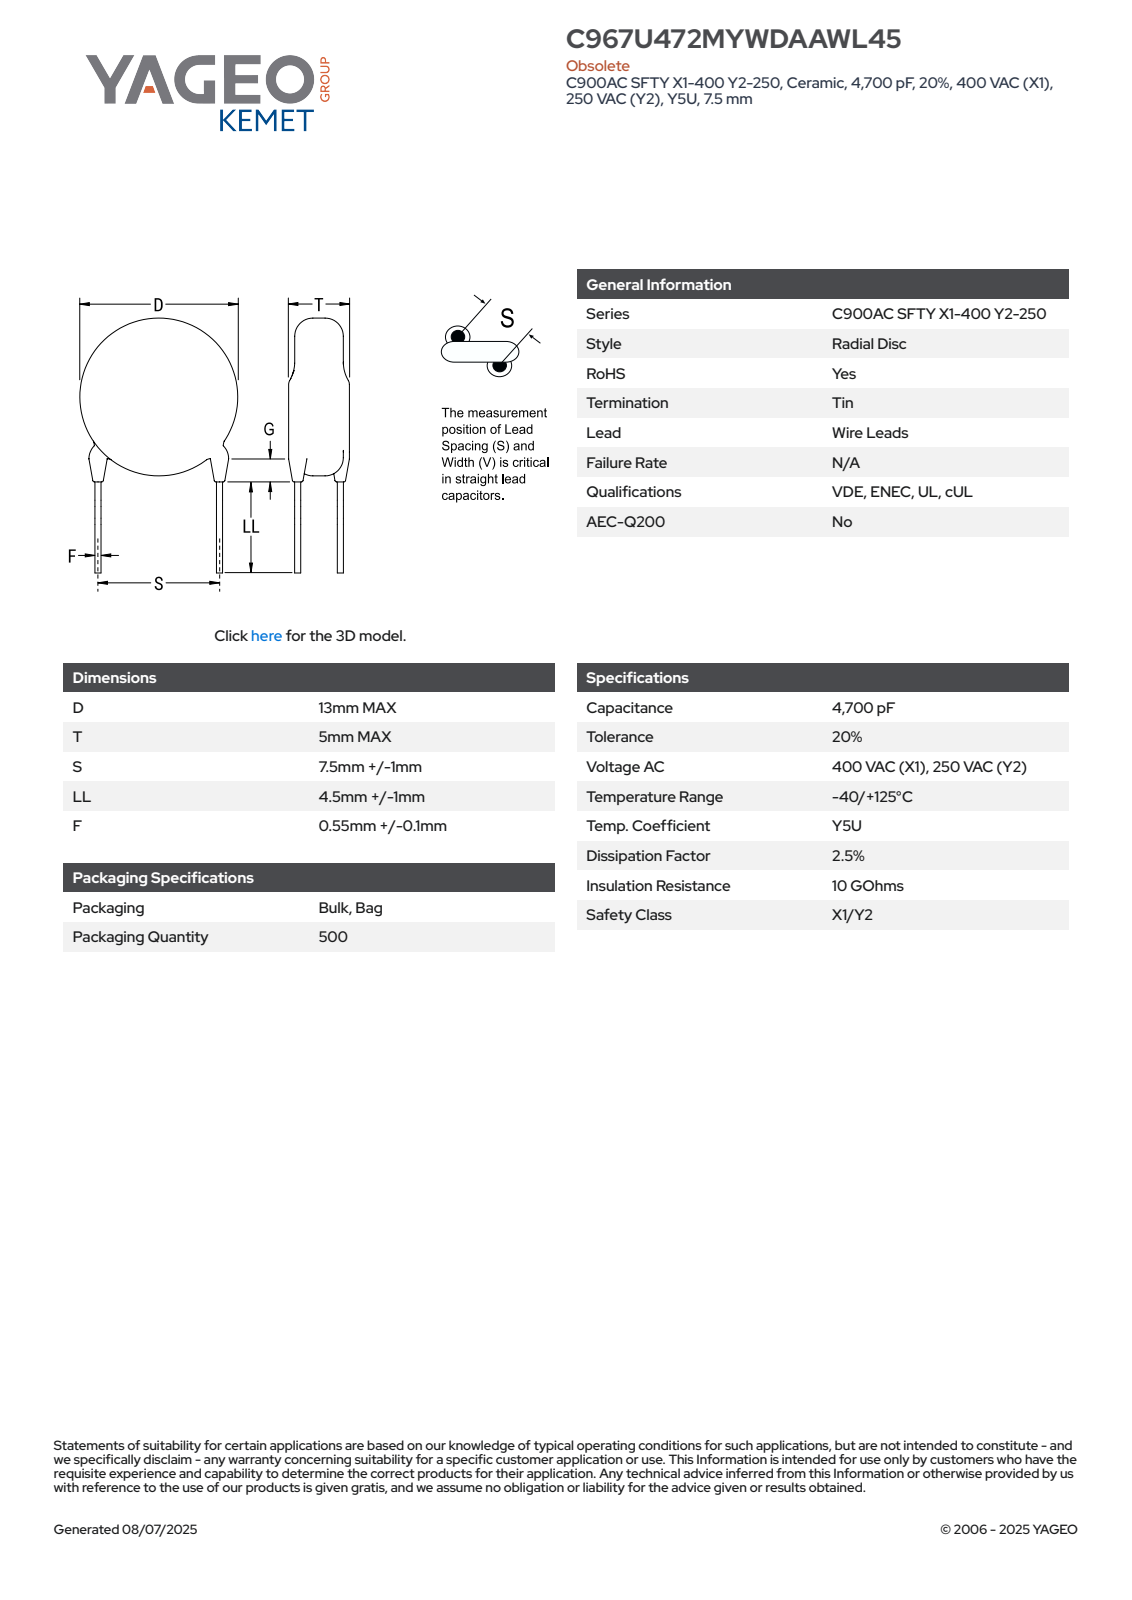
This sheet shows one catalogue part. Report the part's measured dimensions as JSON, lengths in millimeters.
{"part_name": "CCD_STC900_D13T5S7.5LL5.5F0.65G3", "step_written_by": "SolidWorks 2014 (AUTOMOTIVE_DESIGN)", "units": "millimeters", "bodies": {"solids": 4, "faces": 83, "planar": 61, "cylindrical": 6, "other": 16}, "overall_size": [18.73, 13, 5], "volume_mm3": 652, "surface_area_mm2": 476, "round_bosses_or_shafts": [[0.65, 2], [13, 1]], "face_to_face_distances": [5, 1.5, 12.98, 11.48, 0.41, 6.13, 0.93, 3.1, 4.45, 4.63]}
